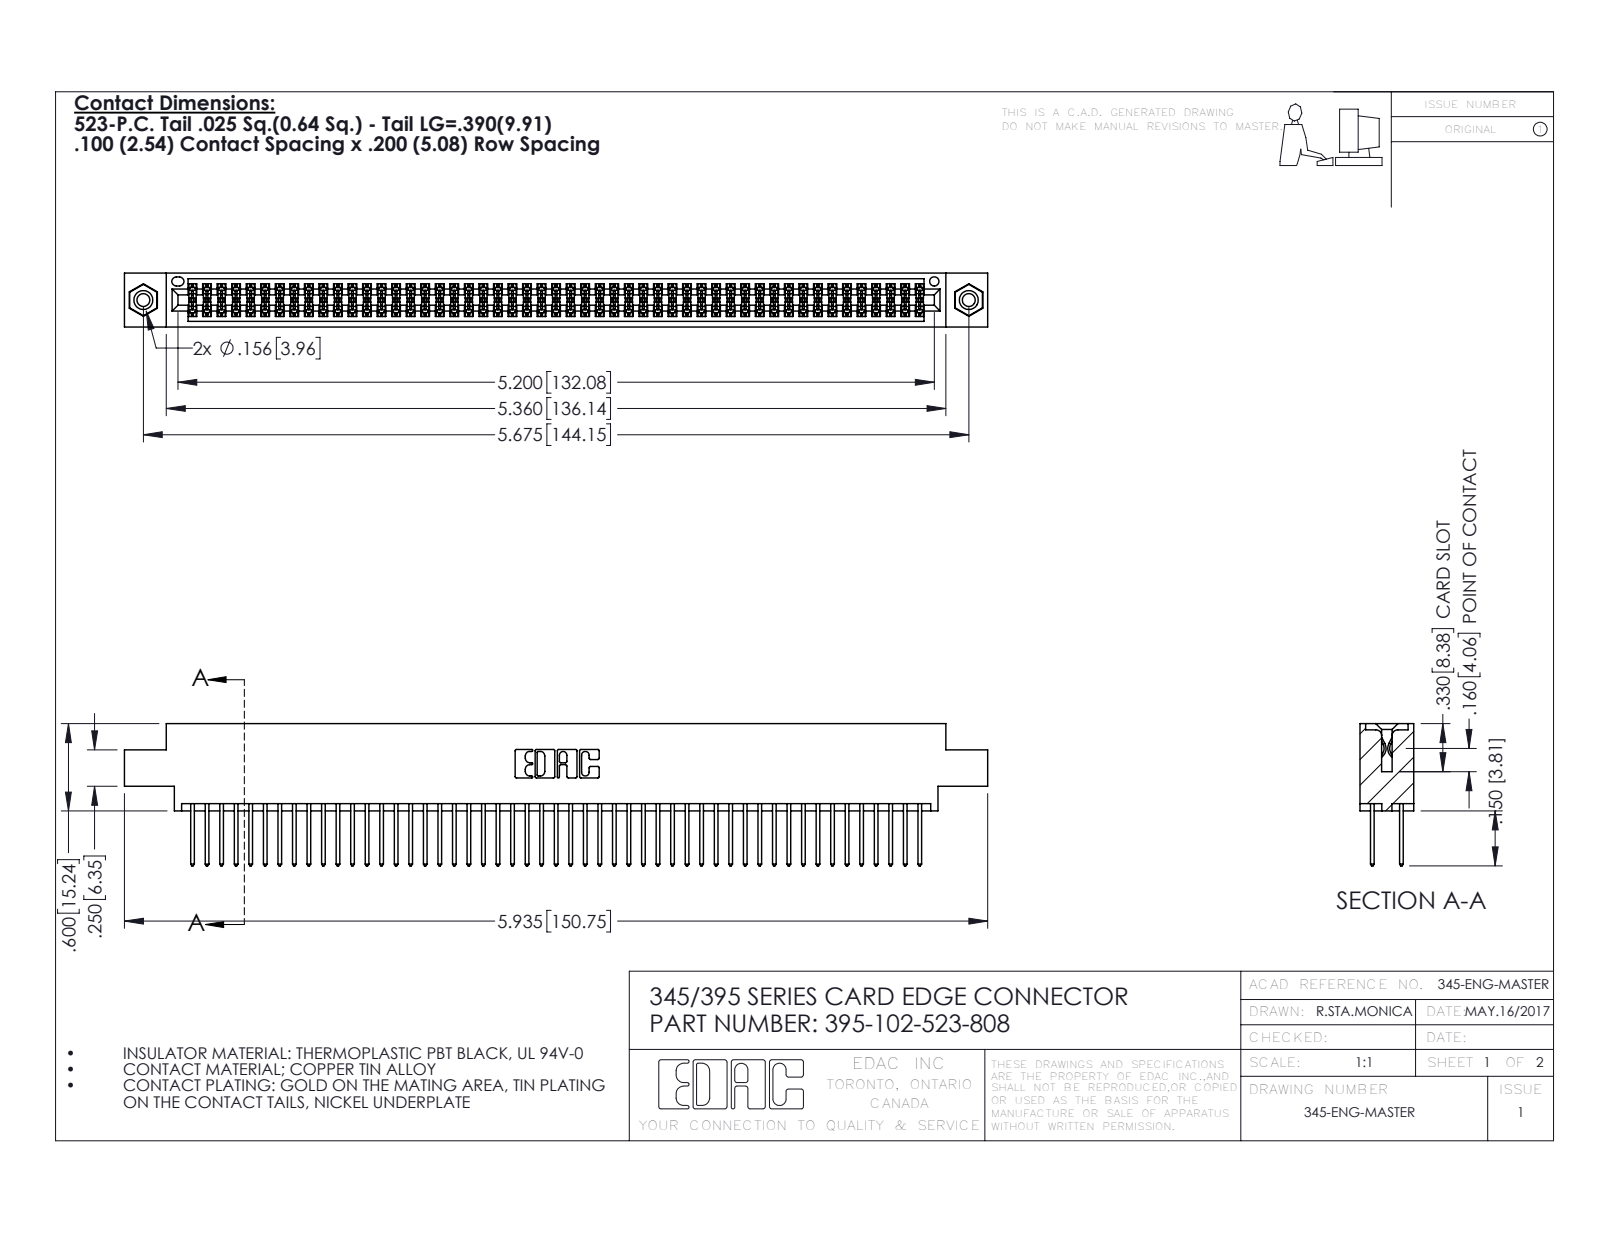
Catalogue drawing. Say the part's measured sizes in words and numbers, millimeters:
The part is named "395-102-523-808; 345 Part_0.170 Offset - 0.156 Dia-TI; 345-292-001_345-293-123; 345-250-001_345-250-003-102". Its 3-D file was written by "SolidWorks 2016 (CONFIG_CONTROL_DESIGN)". It is 105 solids with 5290 faces: 3482 planar, 1792 cylindrical and 16 other. Overall it measures 150.7 by 24.8 by 9.4 millimeters. Its volume is 14 800 cubic millimeters and its surface area 23 170 square millimeters. Round holes: 2 of diameter 2.3, 2 of diameter 3.2, 2 of diameter 4, 1 of diameter 1.6. Round bosses or shafts: 2 of diameter 3.9. Partial cylindrical surfaces (rounded edges, fillets, slot ends): 153 of radius 0.2, 102 of radius 0.3, 22 of radius 0.3, 6 of radius 0.2, 6 of radius 0.8, 3 of radius 0.7, 2 of radius 0.4, 2 of radius 0.5. The main face-to-face distances are 1.8, 7.6, 5.1, 2.5, 6.9, 0.6, 9.4, 5.7, 4.4, 3.8. The hole center spacings are 6.9, 138.2, 144.1.
